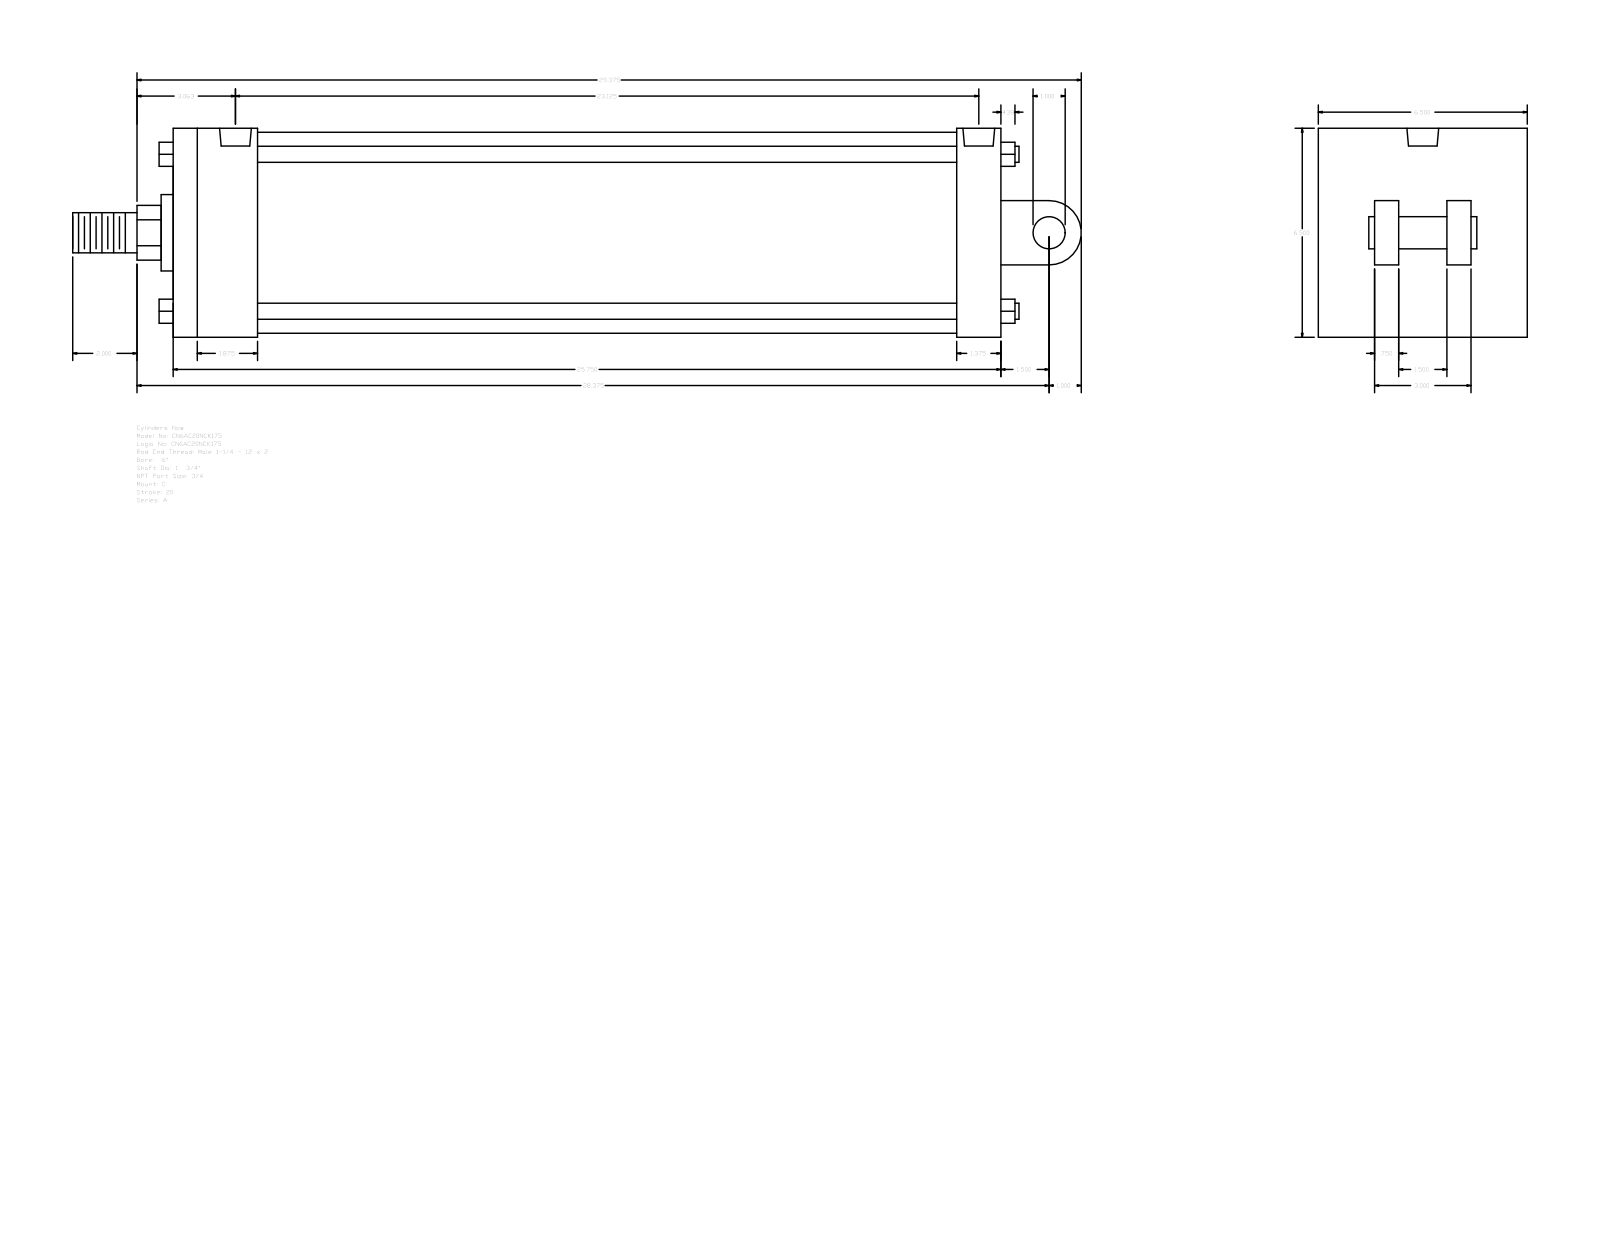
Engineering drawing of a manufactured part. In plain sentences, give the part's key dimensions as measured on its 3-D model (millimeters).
The part is named "A_C__0600_1.75". Its 3-D file was written by "GSSL Pune (CONFIG_CONTROL_DESIGN)". It is 0 solids with 135 faces: 102 planar, 33 cylindrical and 0 other. Overall it measures 796.92 by 165.1 by 165.1 millimeters. Round holes: 4 of diameter 15.08, 2 of diameter 25.12. Round bosses or shafts: 4 of diameter 12.7, 1 of diameter 158.75, 1 of diameter 60.33, 1 of diameter 44.45, 1 of diameter 31.75, 1 of diameter 25.4. Partial cylindrical surfaces (rounded edges, fillets, slot ends): 1 of radius 21.63, 1 of radius 25.4. The main face-to-face distances are 165.1, 654.05, 19.05, 57.15, 66.68, 587.37, 619.13, 552.45, 34.92, 63.5. The hole center spacings are 5.56, 576.25, 581.81, 587.37.
